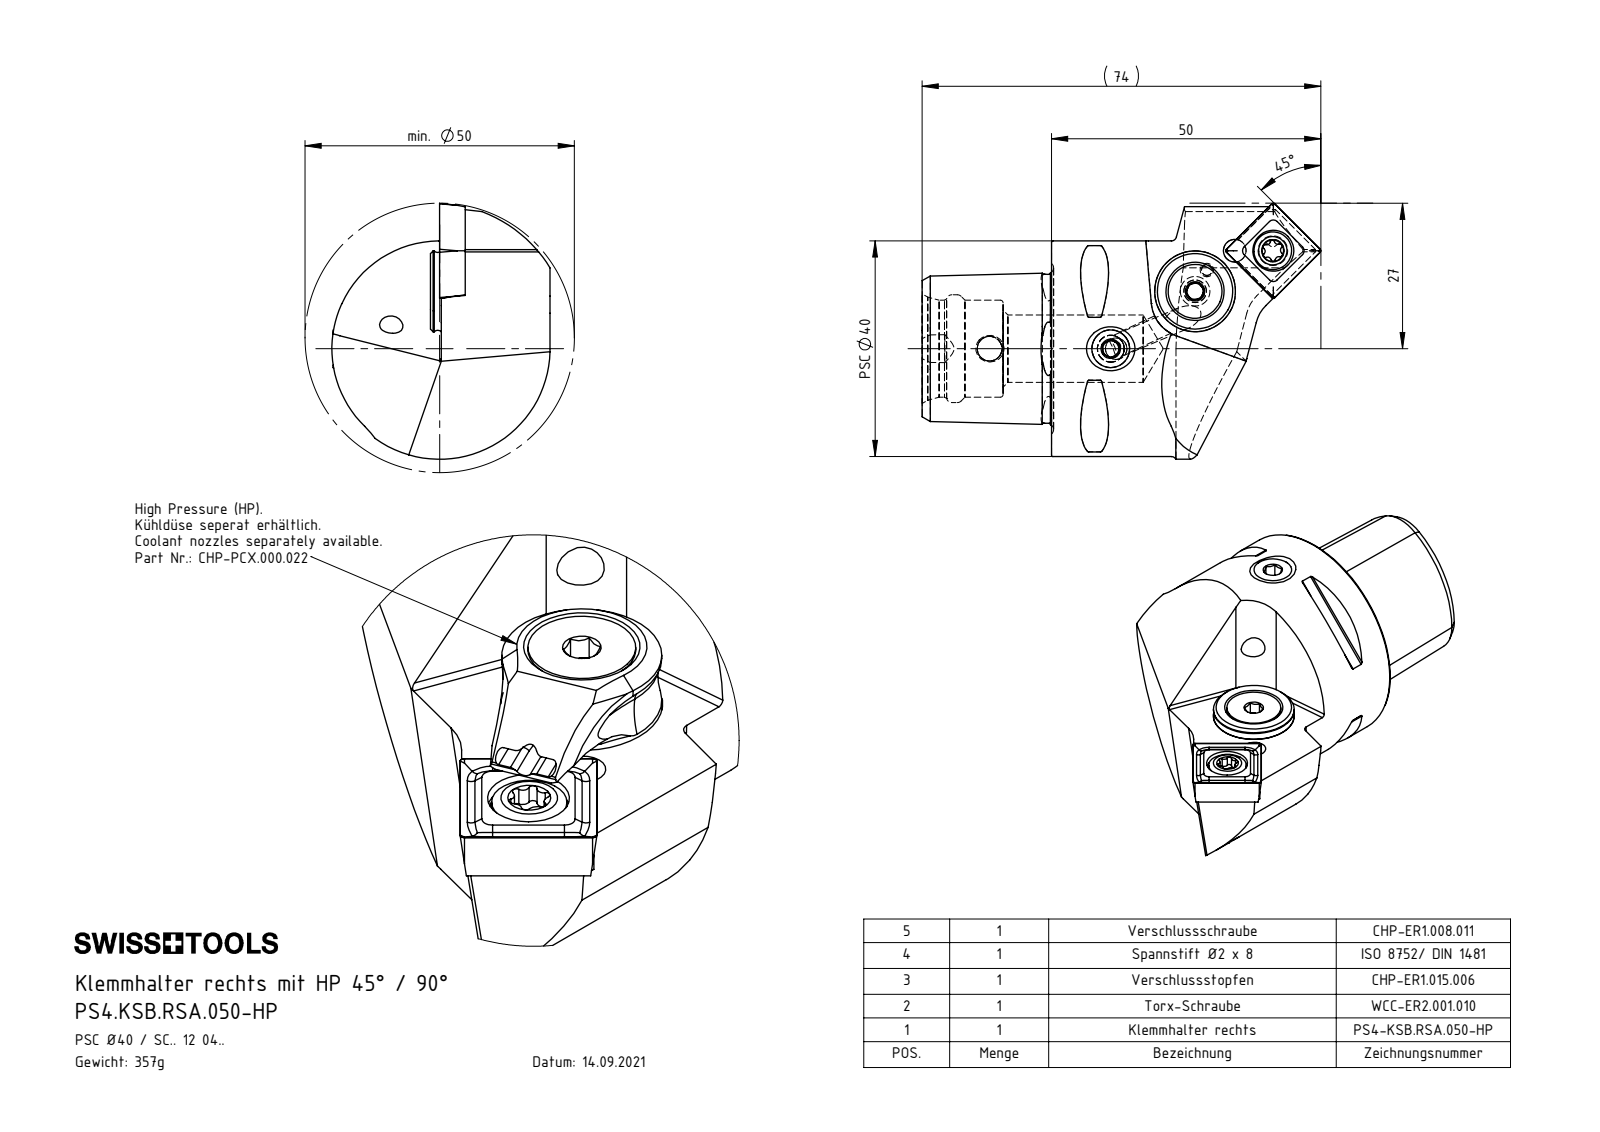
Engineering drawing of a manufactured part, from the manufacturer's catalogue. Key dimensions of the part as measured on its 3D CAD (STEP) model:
Part name (STEP PRODUCT): PS4-KSB.RSA.050-HP_A_frsen; CHP-PCX.000.022_Dse; DIN 7991 - M5x18; DIN 3771 - 6.5x1.5 (+7 more)
STEP written by: SolidWorks 2017 (AUTOMOTIVE_DESIGN)
Units: millimetres
Bodies: 10 solids, 498 faces (110 planar, 136 cylindrical, 252 other)
Overall size (bounding box): 74 × 47.5 × 40.5
Volume: 47 079 mm³ · Surface area: 16 538 mm²
Round holes (diameter × count): ⌀4.2 ×5, ⌀1.2 ×1, ⌀2 ×1, ⌀3 ×1, ⌀4 ×1, ⌀4.6 ×1, ⌀5 ×1, ⌀5.3 ×1, ⌀5.5 ×1, ⌀7 ×1, ⌀7.6 ×1, ⌀12.5 ×1
Round bosses / shafts (diameter × count): ⌀5 ×2, ⌀40 ×1, ⌀14.85 ×1, ⌀13.4 ×1, ⌀10 ×1, ⌀8 ×1, ⌀7 ×1, ⌀5.5 ×1
Partial cylindrical surfaces — rounded edges, fillets, slot ends (radius × count): R0.3 ×9, R1 ×7, R0.39 ×6, R0.5 ×4, R0.69 ×3, R0.69 ×3, R6 ×3, R1.1 ×2
Main face-to-face distances: 4.46, 15.74, 20.2, 24, 15.7, 4.5, 15.52, 1.5, 3, 17.2
Hole centre spacings: 1, 4.51, 6.3, 7.08, 7.18, 10.54, 12.77, 12.86
